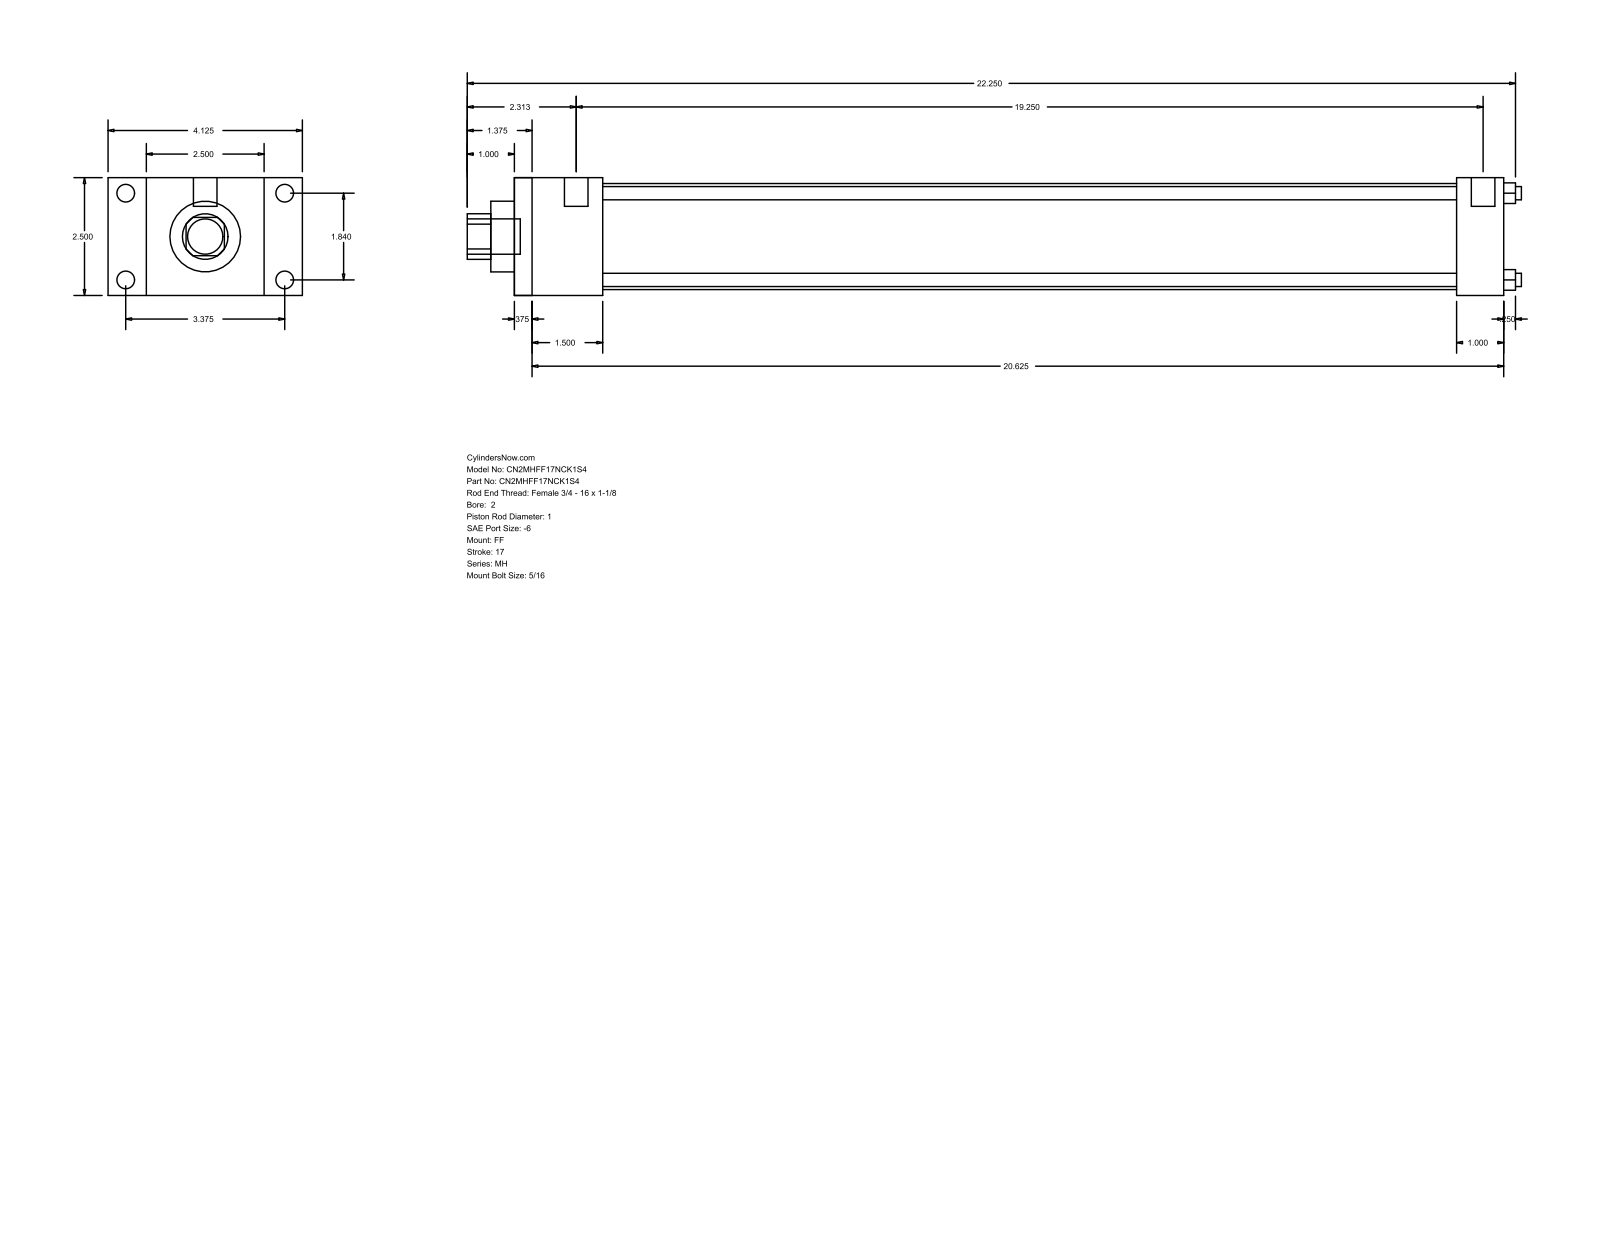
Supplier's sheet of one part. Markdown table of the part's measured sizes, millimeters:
| quantity | value |
| --- | --- |
| part name | MH_FF__0200_1 |
| STEP written by | GSSL Pune (CONFIG_CONTROL_DESIGN) |
| units | millimeters |
| bodies | 0 solids, 92 faces (64 planar, 28 cylindrical, 0 other) |
| overall size | 568.33 × 104.78 × 63.5 |
| round holes (diameter × count) | 7.14 × 4, 25.4 × 1, 38.1 × 1, 57.15 × 1 |
| round bosses / shafts (diameter × count) | 9.53 × 4, 5.56 × 4, 12.7 × 2, 19.05 × 1 |
| partial cylindrical surfaces (radius × count) | 12.29 × 1 |
| main face-to-face distances | 63.5, 533.4, 9.52, 523.88, 20.64, 25.4, 47.63, 508, 38.11, 498.48 |
| hole center spacings | 33.05, 46.74, 66.1 |
